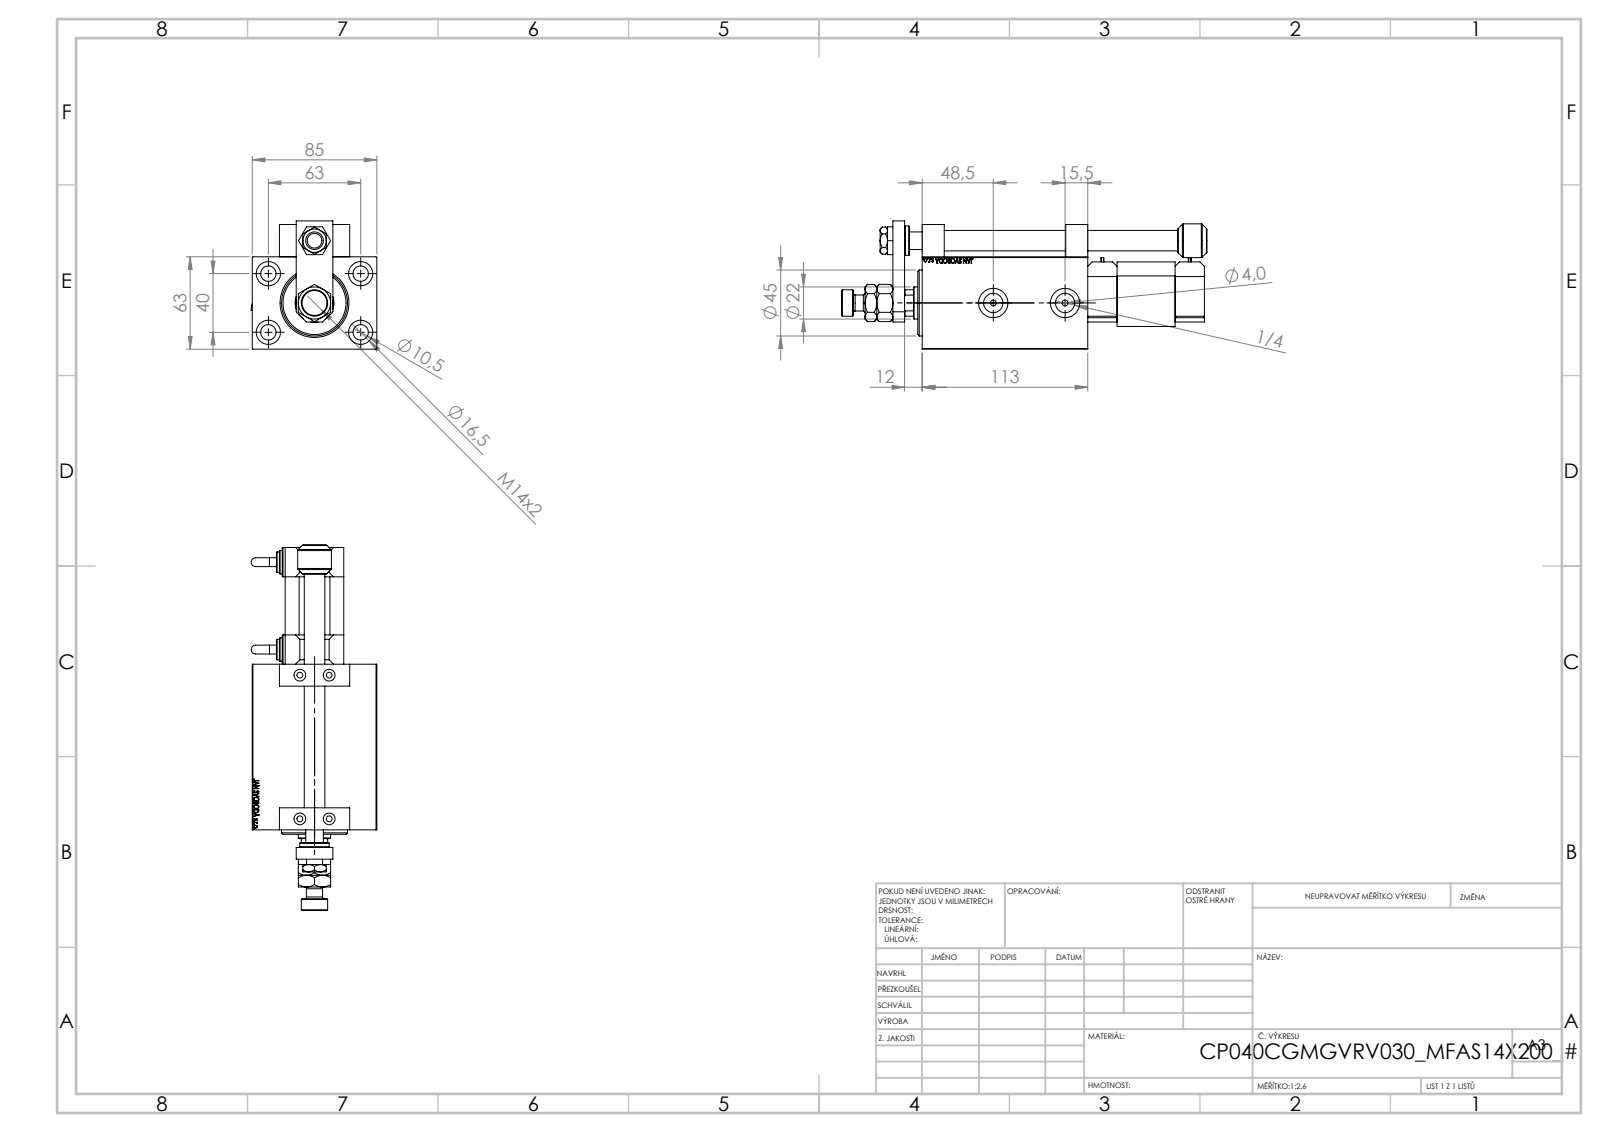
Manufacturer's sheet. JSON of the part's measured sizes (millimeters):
{"part_name": "SWITCH DIM W_B; V450CP_B_VCP; P_V_Z_MFA; ZARAZKA_P (+7 more)", "step_written_by": "SolidWorks 2019 (CONFIG_CONTROL_DESIGN)", "units": "millimeters", "bodies": {"solids": 15, "faces": 1162, "planar": 541, "cylindrical": 136, "other": 485}, "overall_size": [249.4, 87.5, 85.76], "volume_mm3": 744849, "surface_area_mm2": 154843, "round_holes": [[4, 8], [16.5, 5], [8, 4], [10.5, 4], [9.73, 2], [13.16, 2], [14, 2], [15, 2], [20, 2], [12, 1], [12.5, 1], [13, 1]], "round_bosses_or_shafts": [[20, 3], [16, 2], [14, 2], [6, 2], [23, 1], [18, 1], [11, 1]], "partial_cylinders_radius": [[3, 1], [10.5, 1]], "face_to_face_distances": [63, 85, 20, 113, 133, 62.5, 22.5, 59.6, 12, 44], "hole_center_spacings": [37.31, 20, 38.71, 39.3, 40, 63, 69.99, 70.88]}
